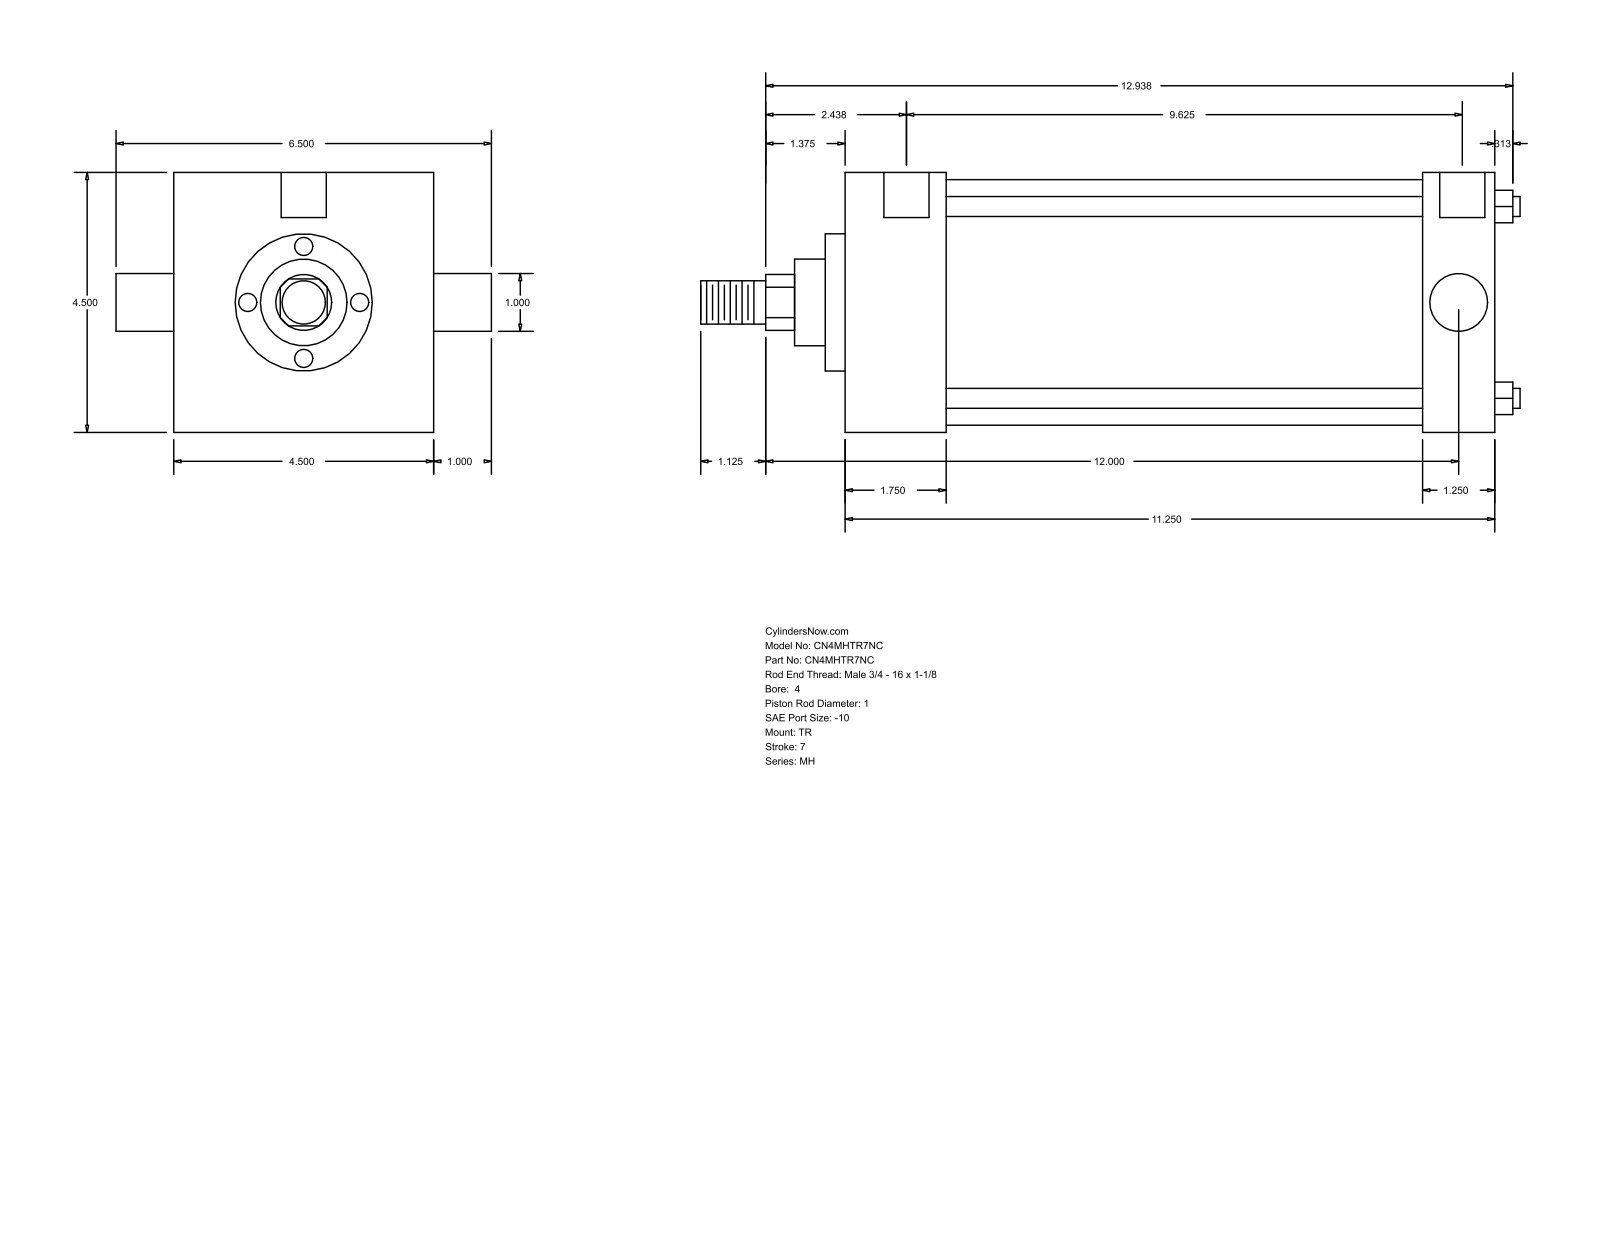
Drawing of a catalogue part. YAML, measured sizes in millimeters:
part_name: "MH_TR__0400_1"
step_written_by: "GSSL Pune (CONFIG_CONTROL_DESIGN)"
units: millimeters
bodies: {solids: 0, faces: 86, planar: 61, cylindrical: 25, other: 0}
overall_size: [360.36, 165.1, 114.3]
round_holes:
  - {diameter: 8.73, count: 3}
  - {diameter: 19.84, count: 2}
round_bosses_or_shafts:
  - {diameter: 8.76, count: 4}
  - {diameter: 25.4, count: 2}
  - {diameter: 107.95, count: 1}
  - {diameter: 60.33, count: 1}
  - {diameter: 38.1, count: 1}
  - {diameter: 19.05, count: 1}
partial_cylinders:
  - {radius: 12.29, count: 1}
face_to_face_distances: [114.3, 285.76, 44.46, 241.3, 254.01, 209.55, 31.75, 8.73, 53.19, 262.74]
hole_center_spacings: [1.58, 1.59, 244.48, 246.06, 246.07, 247.65]
